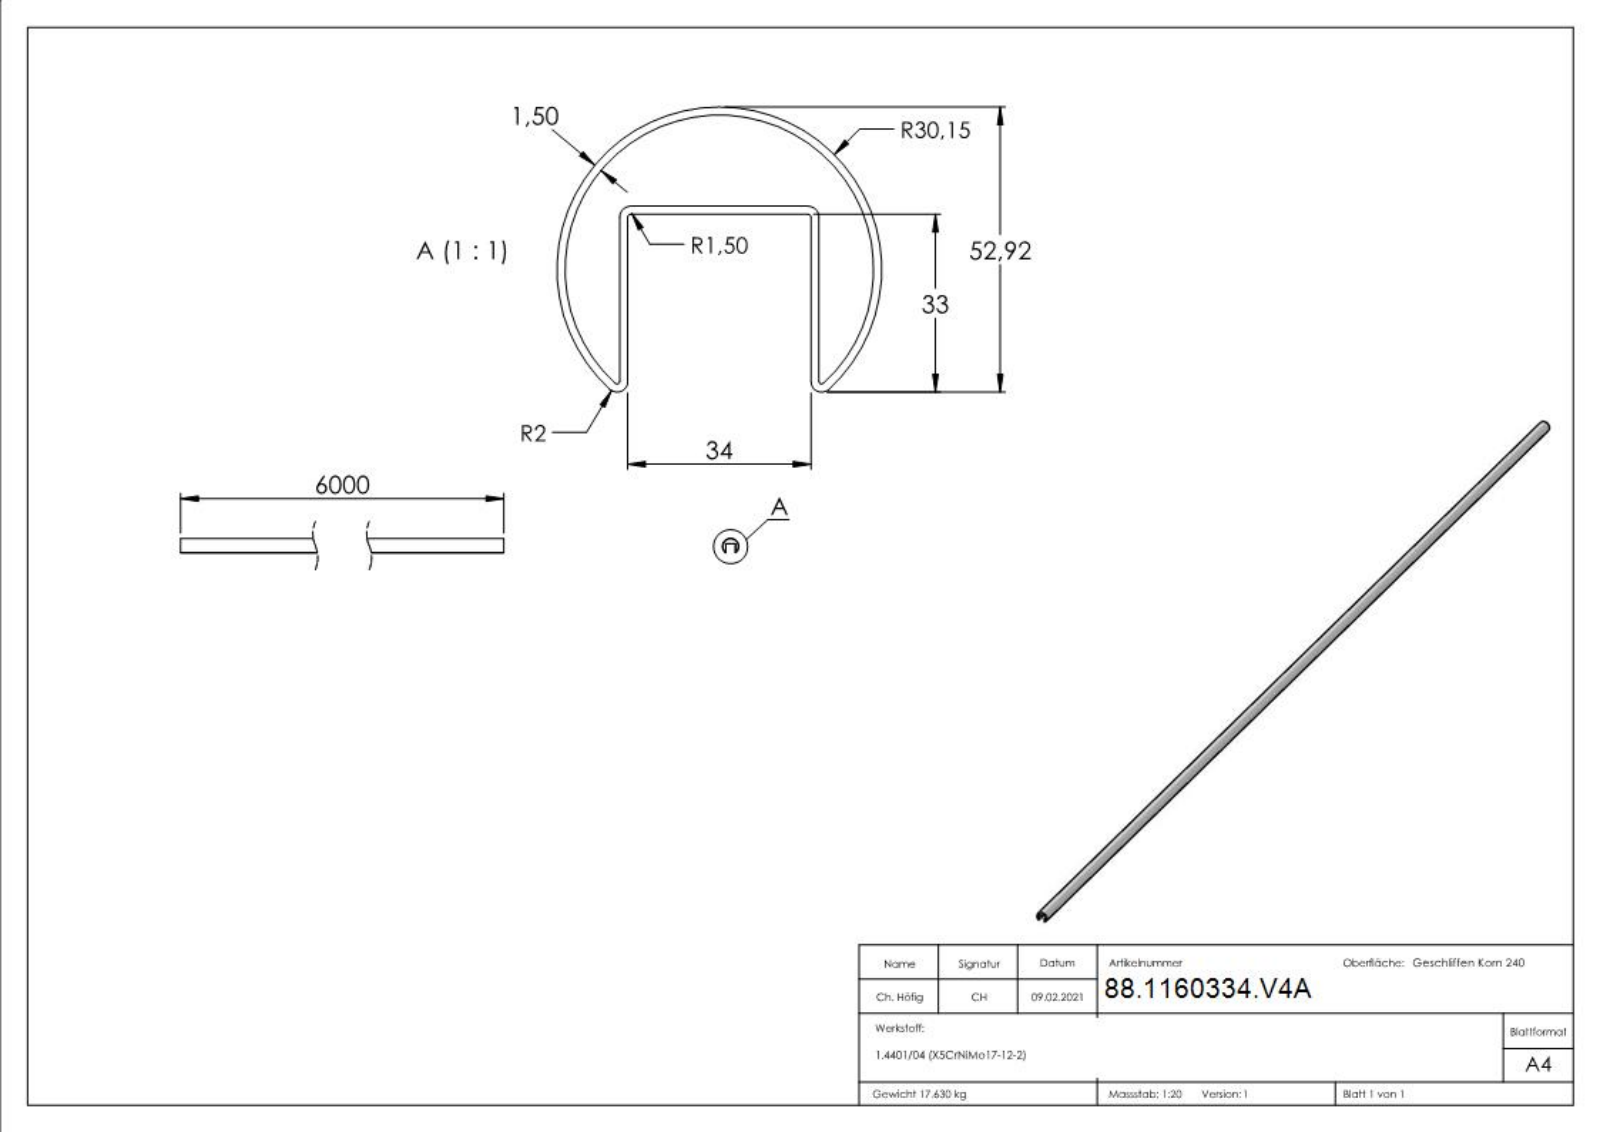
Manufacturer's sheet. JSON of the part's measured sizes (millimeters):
{"part_name": "60334-V4A", "step_written_by": "SolidWorks 2018 (CONFIG_CONTROL_DESIGN)", "units": "millimeters", "bodies": {"solids": 1, "faces": 293, "planar": 165, "cylindrical": 14, "other": 114}, "overall_size": [6000, 60.3, 52.92], "volume_mm3": 2204000, "surface_area_mm2": 2939000, "partial_cylinders_radius": [[0.5, 4], [2, 4], [28.65, 1], [30.15, 1]], "face_to_face_distances": [1.5, 35.5, 34, 37, 6000, 1.4, 0.32, 18.5, 17, 4.9]}
